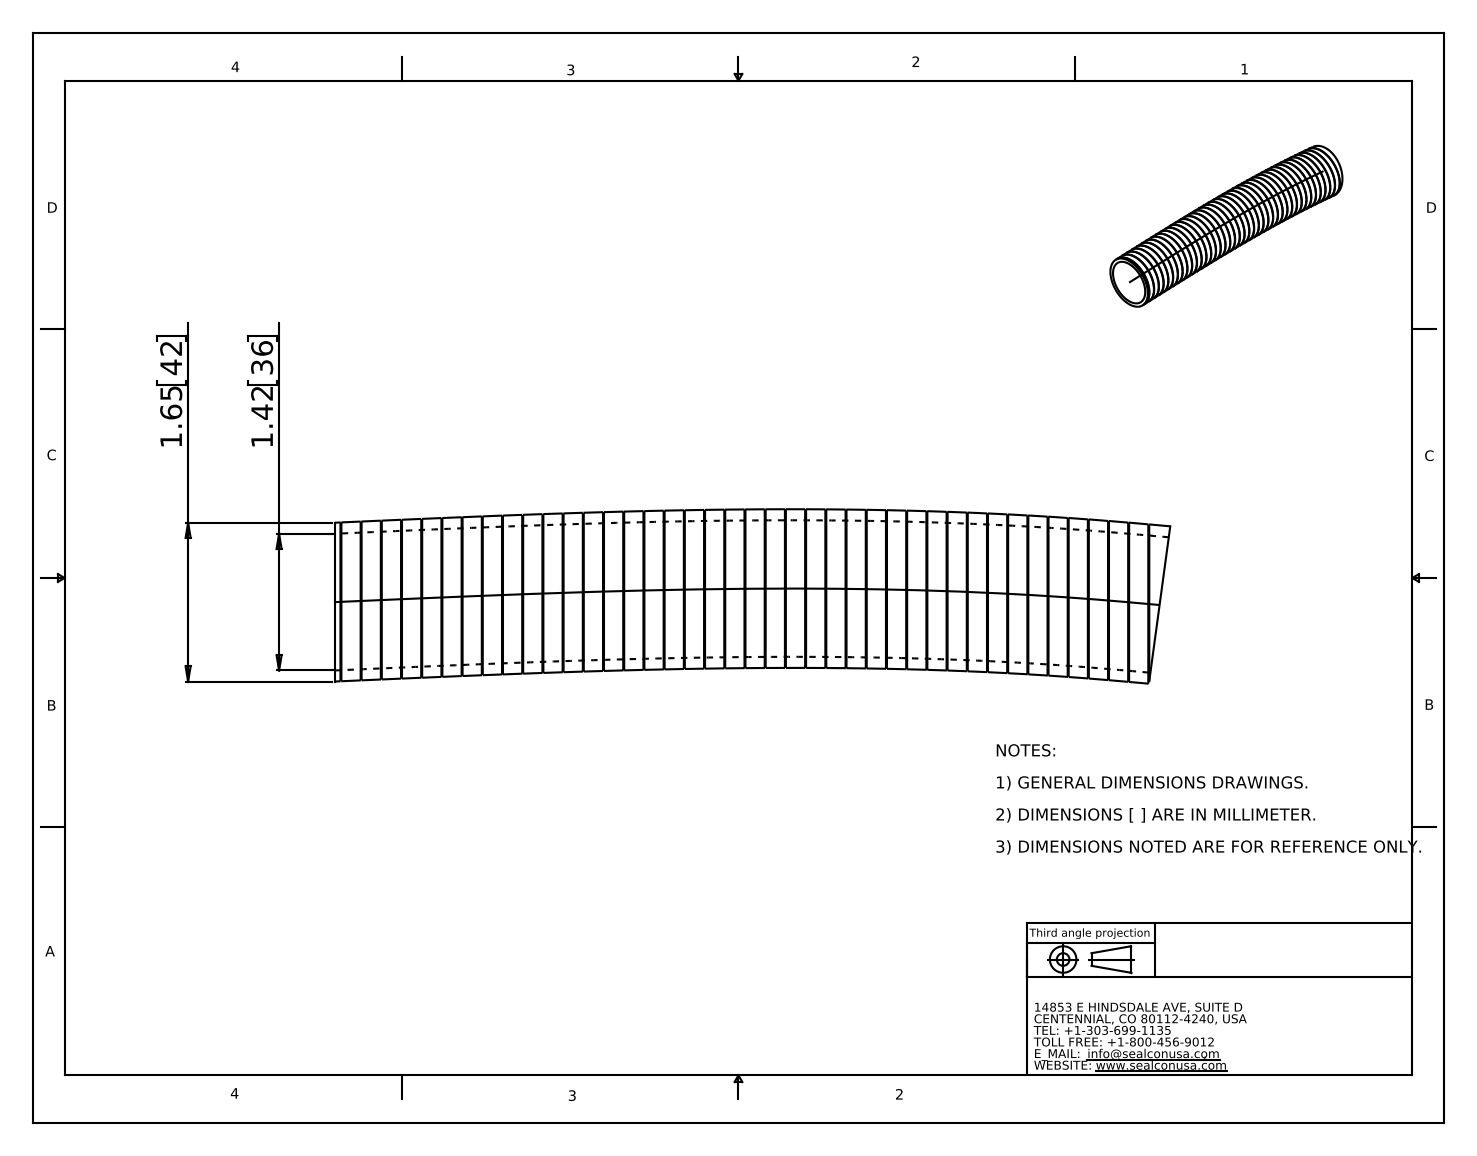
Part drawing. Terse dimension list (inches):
name: SM-1013-HY
written by: SolidWorks 2007 (AUTOMOTIVE_DESIGN)
unit: in
bodies: 1 solid, 253 faces (84 planar, 82 cylindrical, 87 other)
size: 8.681 × 1.812 × 1.65
volume: 4.592 in³; area: 115.9 in²
bosses: 39× ⌀1.49
face distances: 0.209, 0.21, 0.42, 0.199, 0.409, 0.419, 0.63, 0.419, 0.628, 0.22
